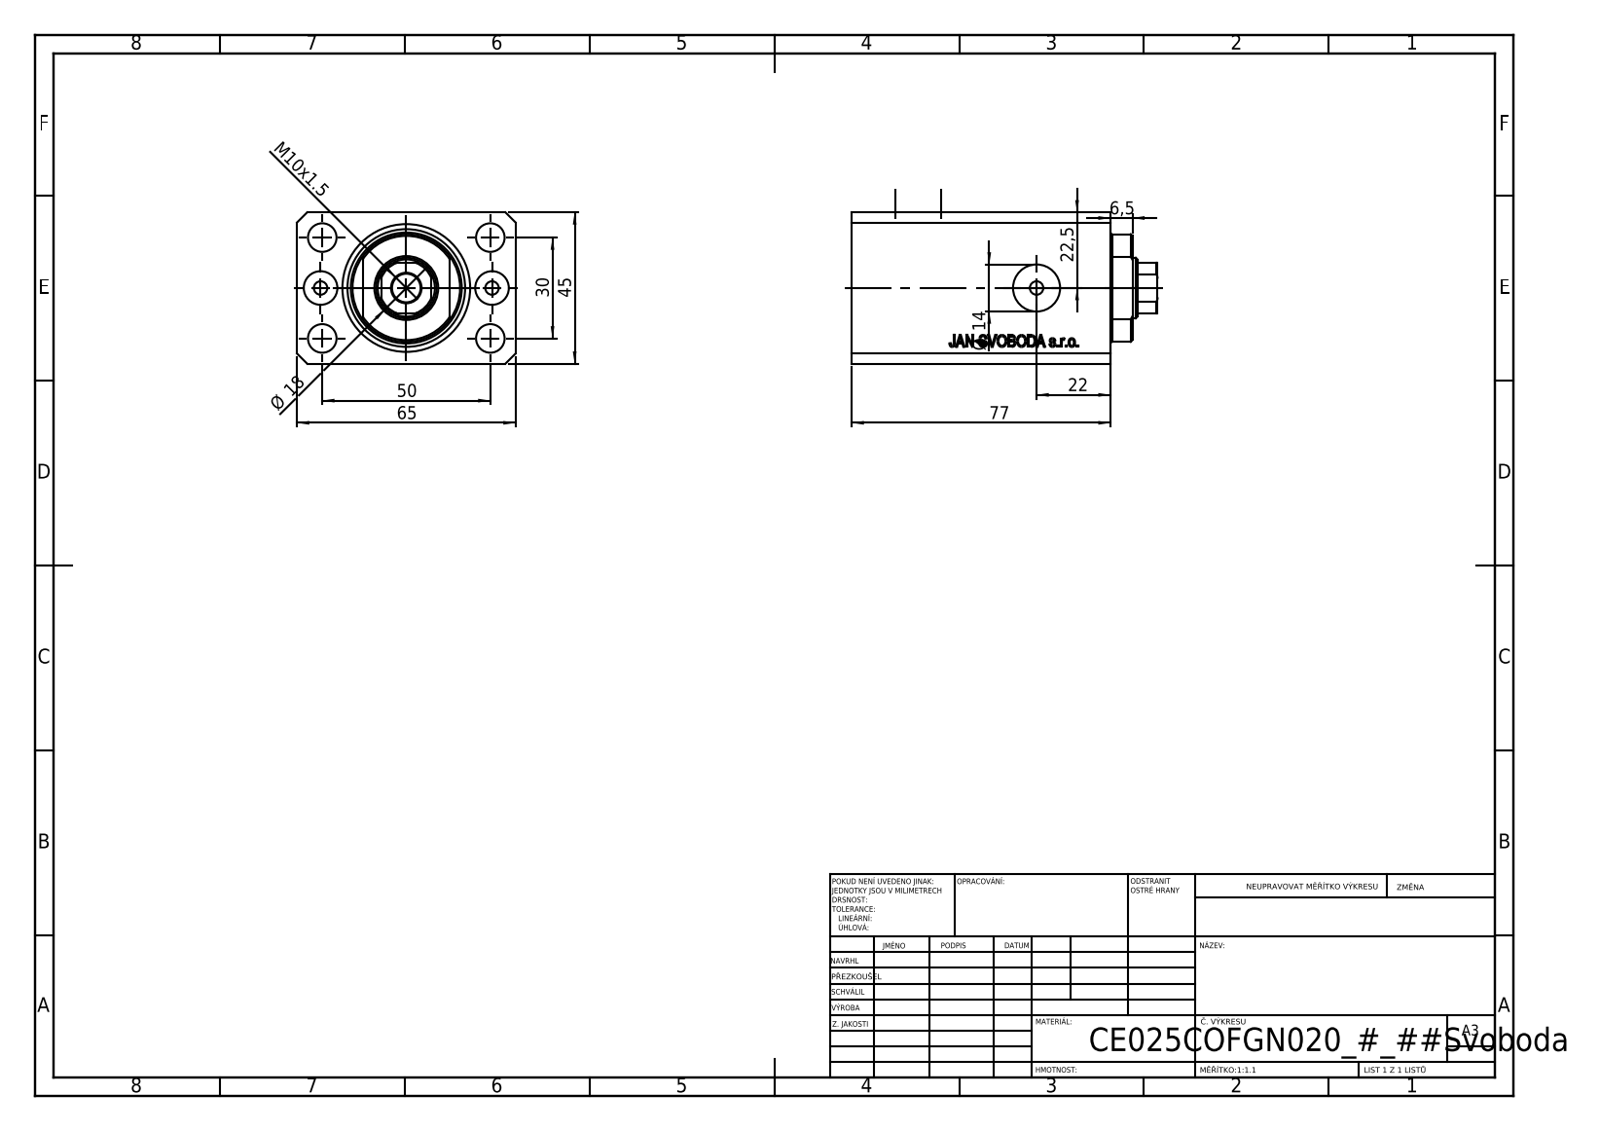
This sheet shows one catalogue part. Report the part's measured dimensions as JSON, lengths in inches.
{"part_name": "V250CE_C_VCP; V250CE_C_Body; V250CE_VC_C", "step_written_by": "SolidWorks 2019 (CONFIG_CONTROL_DESIGN)", "units": "inches", "bodies": {"solids": 3, "faces": 864, "planar": 428, "cylindrical": 44, "other": 392}, "overall_size": [3.583, 2.559, 1.772], "volume_in3": 12.44, "surface_area_in2": 78.03, "round_holes": [[0.335, 5], [0.157, 4], [0.394, 2], [0.551, 2], [0.709, 1], [0.984, 1], [1.496, 1]], "partial_cylinders_radius": [[0.335, 1], [0.63, 1]], "face_to_face_distances": [1.772, 2.559, 0.551, 2.48, 3.031, 0.272, 2.209, 2.76, 2.894, 0.807], "hole_center_spacings": [0.591, 1.148, 2.074, 1.004, 1.181, 1.969, 2.296, 1.299]}
